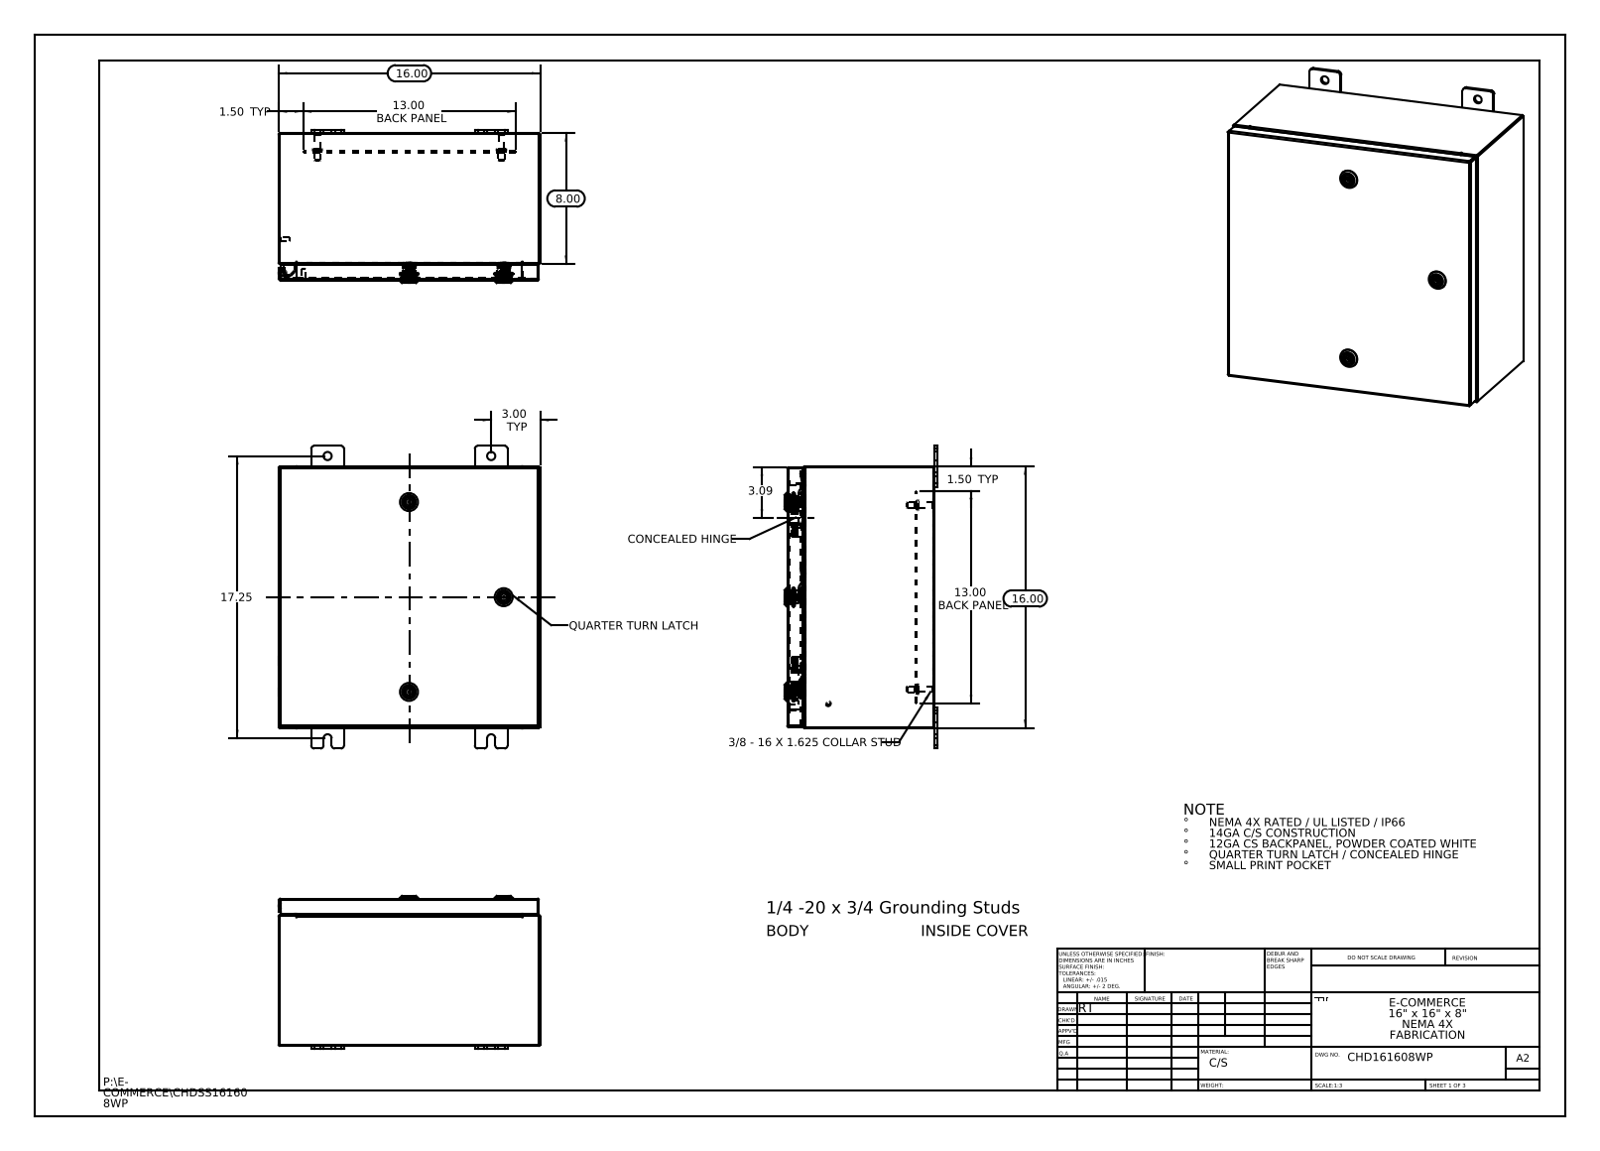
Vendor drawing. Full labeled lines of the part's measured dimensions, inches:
Part name (STEP PRODUCT): HW-CLH-R001-0500_2412-026240-2445-Industrilas; Insert-221320-IB-Industrilas_Insert-221320-IB-Industrilas; CHD161608WP; CHDSS161608WP Body (+8 more)
STEP written by: SolidWorks 2013 (CONFIG_CONTROL_DESIGN)
Units: inches
Bodies: 37 solids, 2966 faces (938 planar, 930 cylindrical, 1098 other)
Overall size (bounding box): 18.5 × 16 × 9.356
Volume: 112.1 in³ · Surface area: 2 835 in²
Round holes (diameter × count): ⌀0.5 ×8, ⌀0.136 ×4, ⌀0.197 ×3, ⌀0.394 ×3, ⌀0.4 ×3, ⌀0.63 ×3, ⌀0.787 ×3, ⌀0.211 ×2
Round bosses / shafts (diameter × count): ⌀0.236 ×5, ⌀0.625 ×4, ⌀0.375 ×4, ⌀0.33 ×4, ⌀1.102 ×3, ⌀0.78 ×3, ⌀0.626 ×3, ⌀0.61 ×3
Partial cylindrical surfaces — rounded edges, fillets, slot ends (radius × count): R0.006 ×99, R0.118 ×99, R0.028 ×36, R0.19 ×24, R0.013 ×18, R0.088 ×18, R0.02 ×12, R0.197 ×12
Main face-to-face distances: 0.075, 15.925, 0.074, 15.85, 16, 9.01, 8.935, 8.936, 8.861, 1
Hole centre spacings: 1.858, 3.065, 5.627, 10, 11.25, 11.25, 12.702, 13.015
